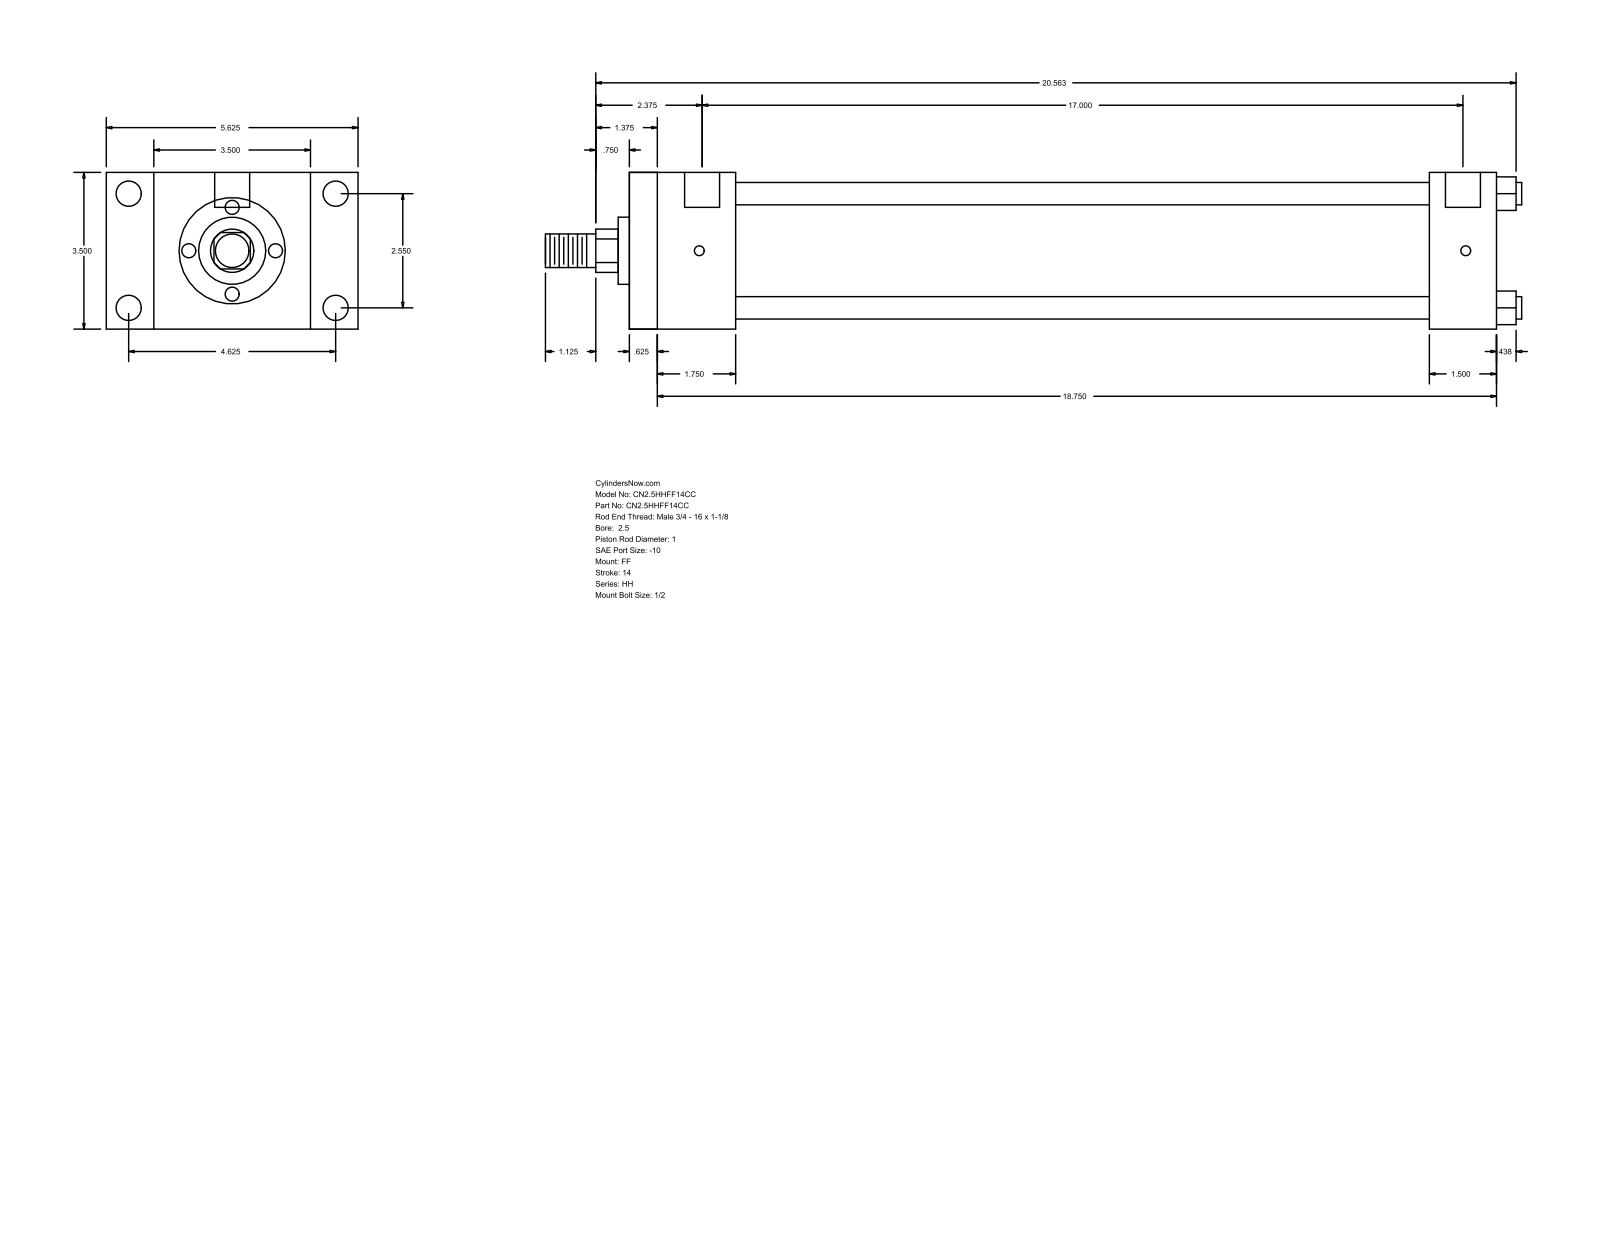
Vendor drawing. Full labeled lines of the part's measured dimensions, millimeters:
Part name (STEP PRODUCT): HH_FF__0250_1
STEP written by: GSSL Pune (CONFIG_CONTROL_DESIGN)
Units: millimetres
Bodies: 0 solids, 92 faces (64 planar, 28 cylindrical, 0 other)
Overall size (bounding box): 554.04 × 142.88 × 88.9
Round holes (diameter × count): ⌀5.56 ×4, ⌀14.3 ×4, ⌀19.84 ×2
Round bosses / shafts (diameter × count): ⌀12.7 ×4, ⌀73.03 ×1, ⌀38.1 ×1, ⌀25.4 ×1, ⌀19.05 ×1
Partial cylindrical surfaces — rounded edges, fillets, slot ends (radius × count): R12.29 ×1
Main face-to-face distances: 88.9, 492.13, 15.87, 476.26, 60.33, 44.46, 431.8, 454.02, 438.15, 393.69
Hole centre spacings: 1.59, 64.76, 117.48, 134.15, 433.38, 434.97, 431.79
